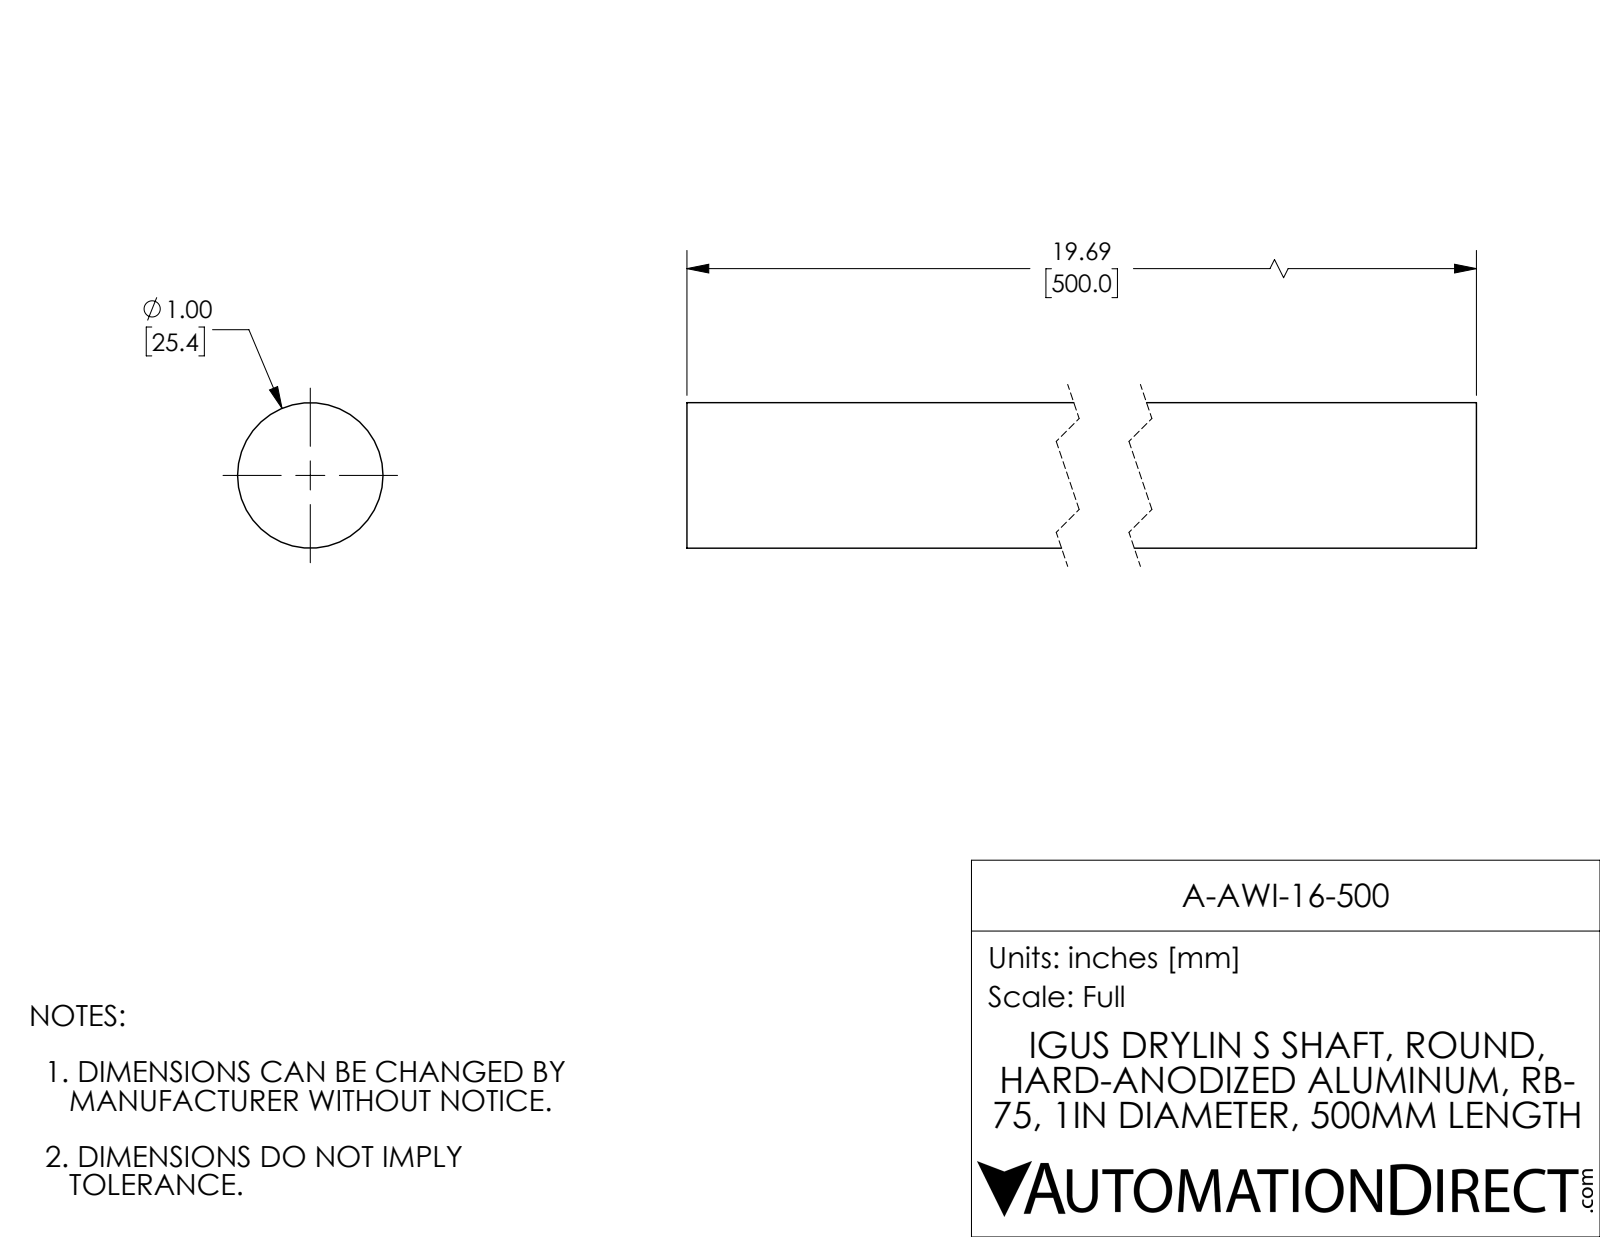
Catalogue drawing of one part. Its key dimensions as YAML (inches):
part_name: "A-AWI-16-500"
step_written_by: "SolidWorks 2017 (AUTOMOTIVE_DESIGN)"
units: inches
bodies: {solids: 1, faces: 4, planar: 2, cylindrical: 2, other: 0}
overall_size: [19.685, 1, 1]
volume: 15.46
surface_area: 63.41
round_bosses_or_shafts:
  - {diameter: 1, count: 1}
face_to_face_distances: [19.685]
